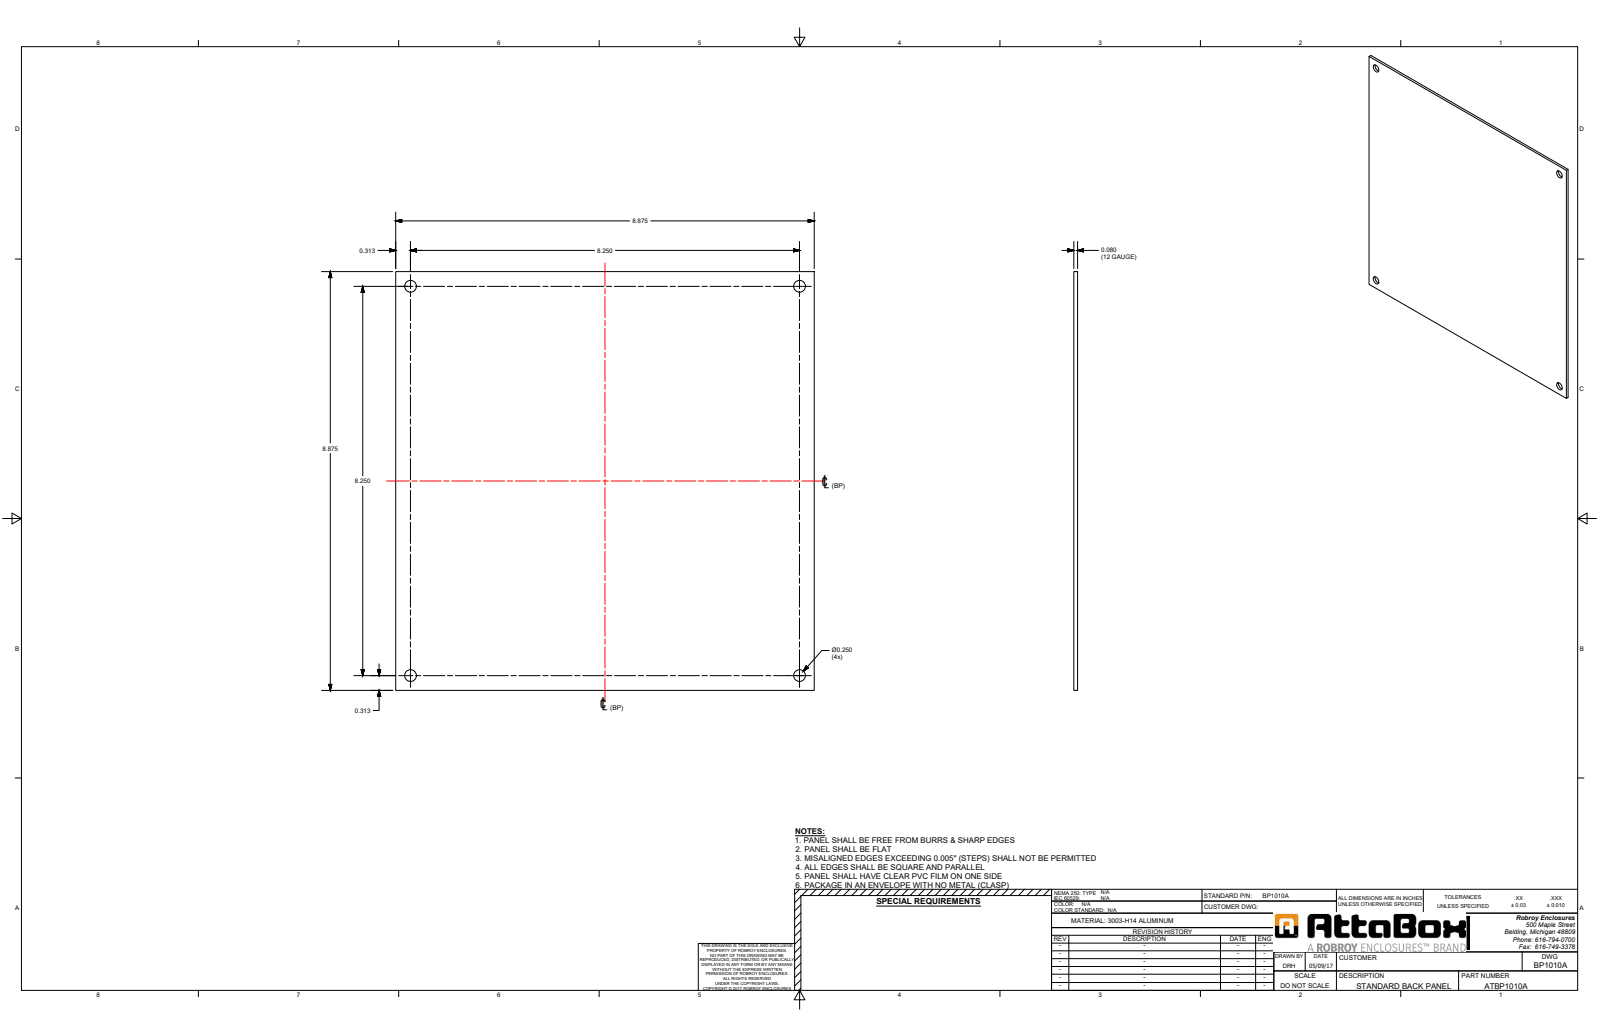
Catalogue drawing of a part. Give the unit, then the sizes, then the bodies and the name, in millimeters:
Units: millimetres
Overall size (bounding box): 225.43 × 225.43 × 2.03
Round holes (diameter × count): ⌀6.35 ×4
Main face-to-face distances: 2.04, 225.42
Hole centre spacings: 209.54, 296.33
Volume: 103 002 mm³ · Surface area: 103 374 mm²
Bodies: 1 solid, 10 faces (6 planar, 4 cylindrical, 0 other)
Part name (STEP PRODUCT): ATBP1010A
STEP written by: Autodesk Inventor 2017 (AUTOMOTIVE_DESIGN)
